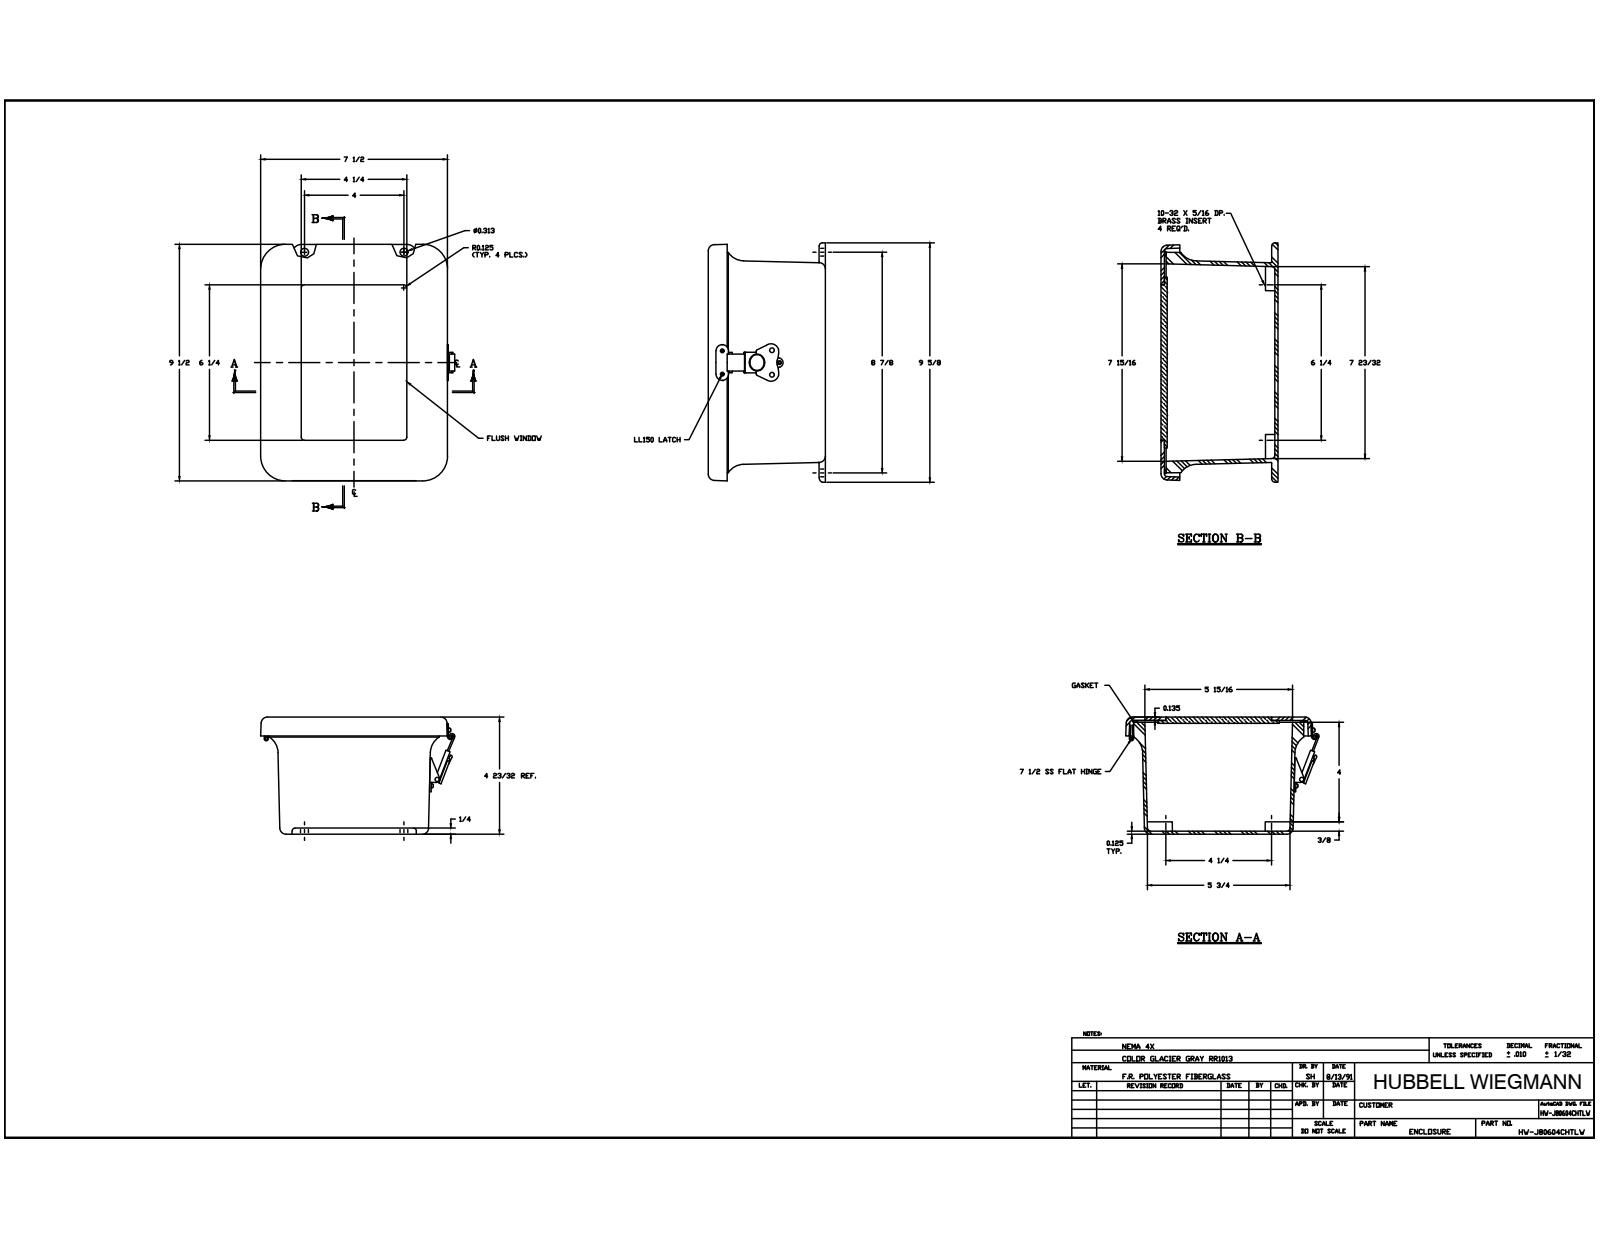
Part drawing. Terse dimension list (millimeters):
name: J806HL_1; RMINS45821P_203; RMINS45821P_204; RMINS45821P_205 (+8 more)
written by: Autodesk Inventor 2014 (AUTOMOTIVE_DESIGN)
unit: mm
bodies: 32 solids, 786 faces (337 planar, 302 cylindrical, 147 other)
size: 244.47 × 196.99 × 119.36
volume: 806 874 mm³; area: 412 512 mm²
holes: 10× ⌀3.56, 6× ⌀3.33, 5× ⌀3.86, 4× ⌀3.96, 4× ⌀5.54, 2× ⌀3.3, 2× ⌀4.2, 2× ⌀5, 1× ⌀2.16, 1× ⌀2.7, 1× ⌀3, 1× ⌀3.5
bosses: 10× ⌀6.35, 10× ⌀3.17, 4× ⌀6.86, 1× ⌀14.8, 1× ⌀13.3, 1× ⌀5.3, 1× ⌀4.7, 1× ⌀3.94
rounds: 20× R0.79, 16× R3.17, 12× R6.35, 10× R2, 4× R0.95, 4× R1, 4× R1.15, 4× R1.2
face distances: 3.18, 3.43, 115.93, 119.36, 3.17, 6.35, 113.01, 112.75, 116.18, 2.92
hole spacings: 88.9, 33.68, 133.89, 184.12, 225.15, 6.36, 82.55, 11.92
